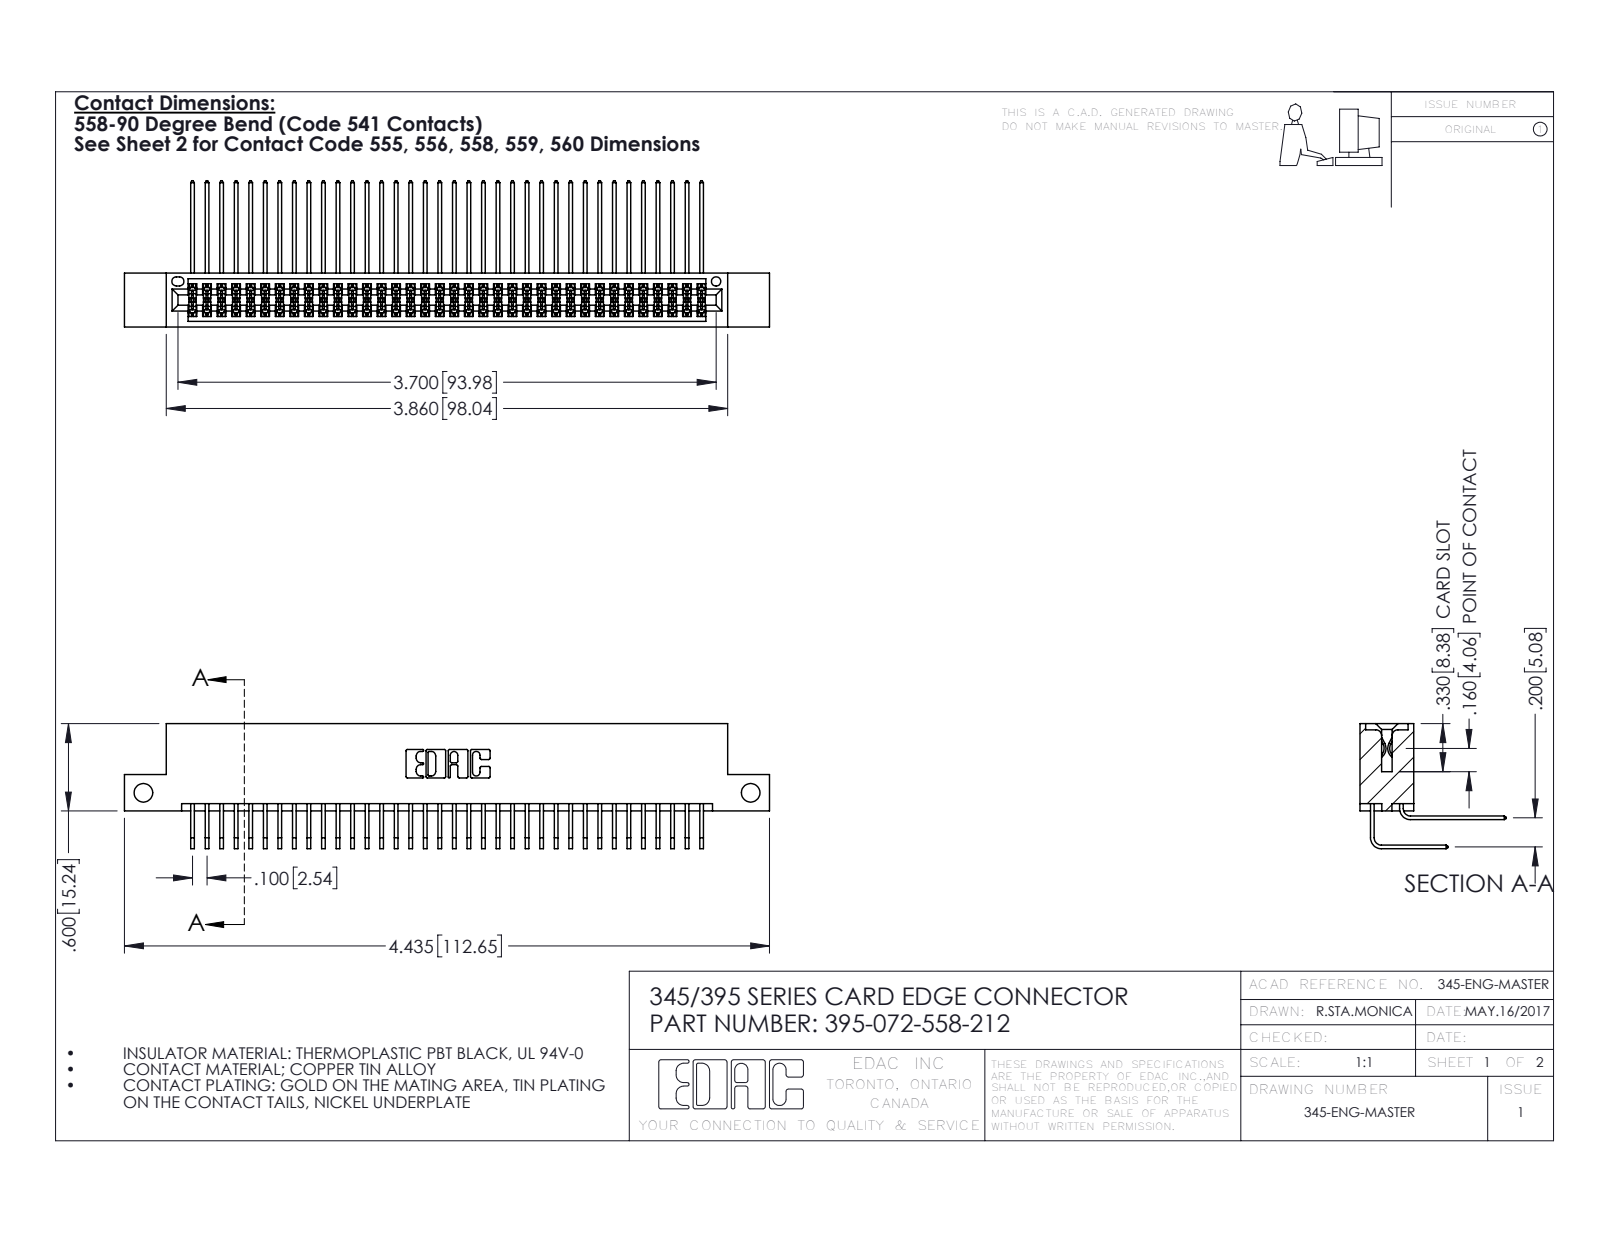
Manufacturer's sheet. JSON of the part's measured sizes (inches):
{"part_name": "345-292-001_558 Tail - 2; 345-292-001_558 559 Tail - 1; 395-072-558-212; 345 Part_Flush Mounting Lugs - Side Mount", "step_written_by": "SolidWorks 2016 (CONFIG_CONTROL_DESIGN)", "units": "inches", "bodies": {"solids": 73, "faces": 3870, "planar": 2600, "cylindrical": 1270, "other": 0}, "overall_size": [4.435, 1.005, 0.859], "volume_in3": 0.684, "surface_area_in2": 28.33, "round_holes": [[0.128, 2], [0.064, 1]], "partial_cylinders_radius": [[0.006, 109], [0.01, 22], [0.007, 6], [0.031, 6], [0.026, 3], [0.014, 2], [0.019, 2], [0.022, 2]], "face_to_face_distances": [0.072, 0.298, 0.2, 0.37, 0.098, 0.272, 0.025, 0.225, 0.025, 0.285], "hole_center_spacings": [4.175]}
